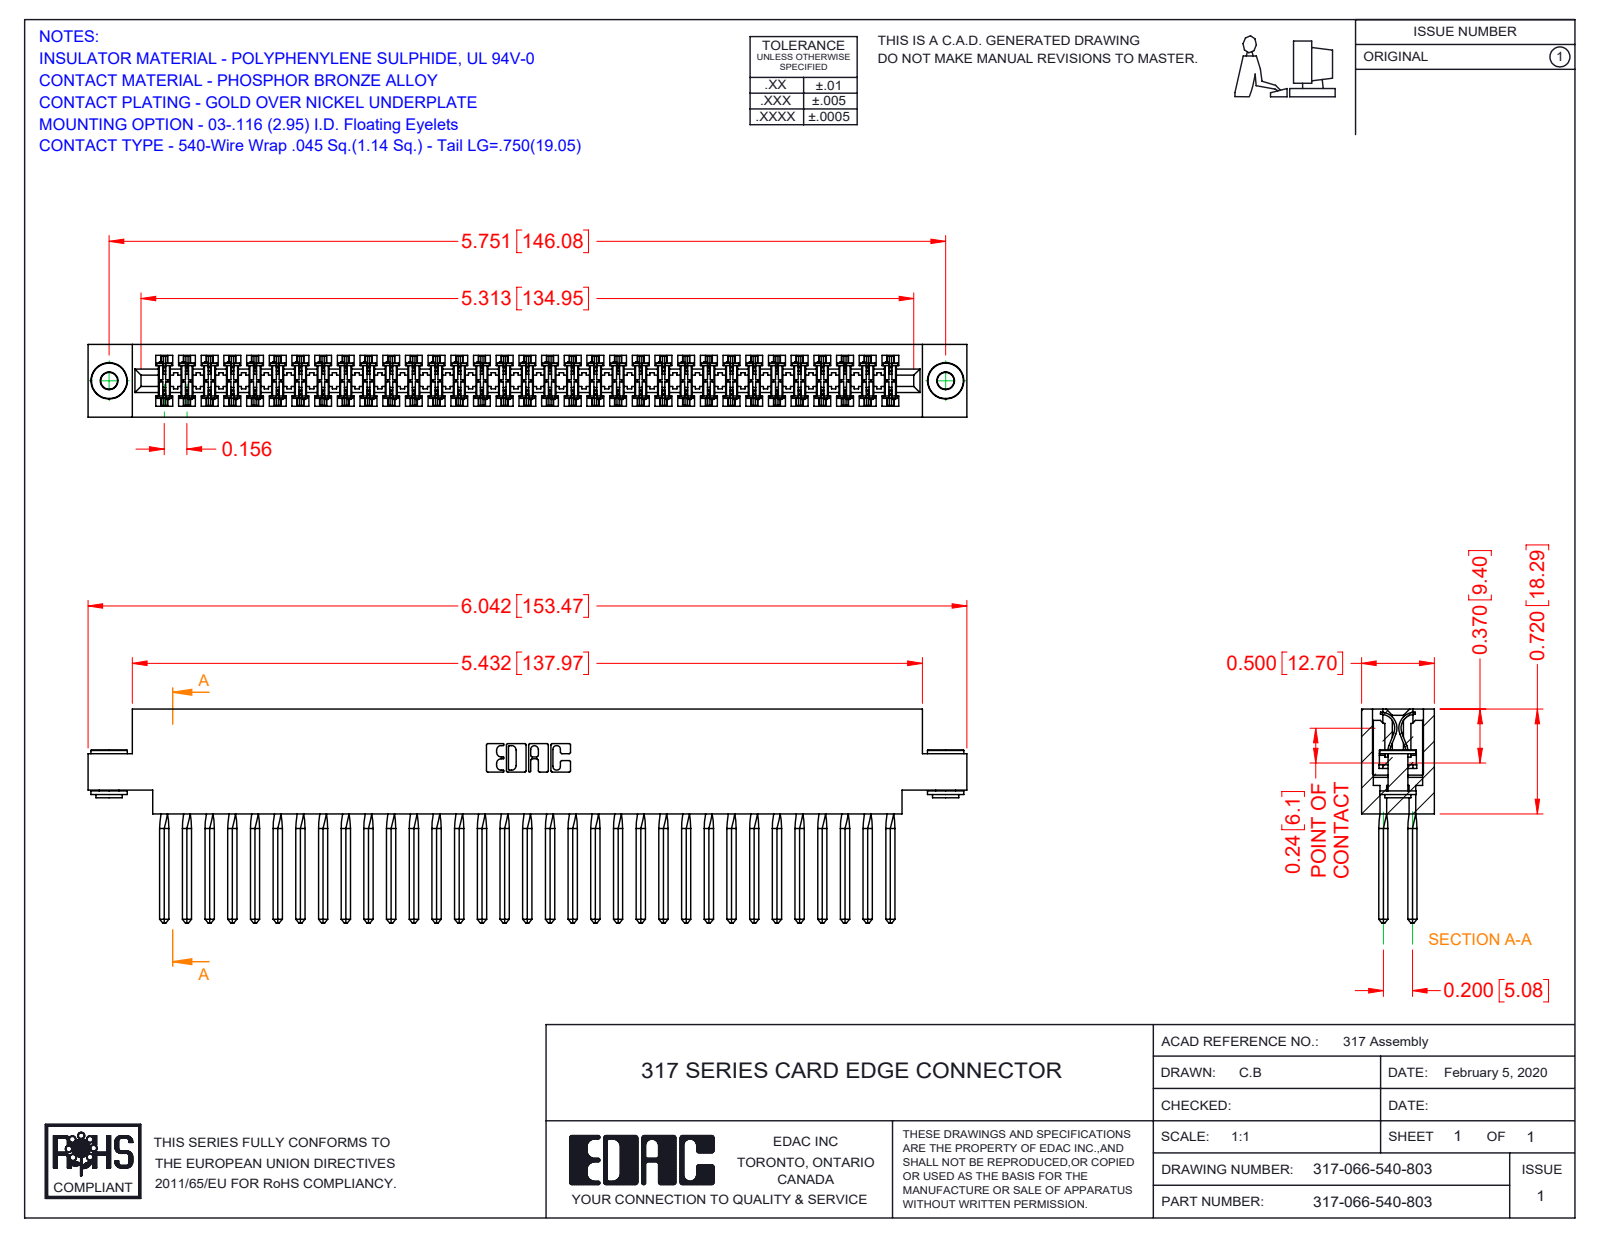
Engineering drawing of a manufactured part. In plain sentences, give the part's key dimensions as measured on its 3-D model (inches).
The part is named "317-066-540-803; 317 Part_.156 Dia - TH; 345-250-002_345-250-002-102; 317-290-001_540". Its 3-D file was written by "SolidWorks 2016 (CONFIG_CONTROL_DESIGN)". It is 69 solids with 6014 faces: 4886 planar, 856 cylindrical and 272 other. Overall it measures 6.042 by 1.47 by 0.5 inches. Its volume is 1.554 cubic inches and its surface area 58.67 square inches. Round holes: 2 of diameter 0.116, 2 of diameter 0.156. Round bosses or shafts: 2 of diameter 0.25, 2 of diameter 0.18, 2 of diameter 0.136. Partial cylindrical surfaces (rounded edges, fillets, slot ends): 132 of radius 0.015, 22 of radius 0.01, 6 of radius 0.007, 6 of radius 0.031, 3 of radius 0.026, 2 of radius 0.095, 2 of radius 0.1, 2 of radius 0.11. The main face-to-face distances are 0.5, 0.075, 0.425, 0.35, 0.11, 0.195, 0.094, 0.2, 0.115, 0.131. The hole center spacings are 5.751.
